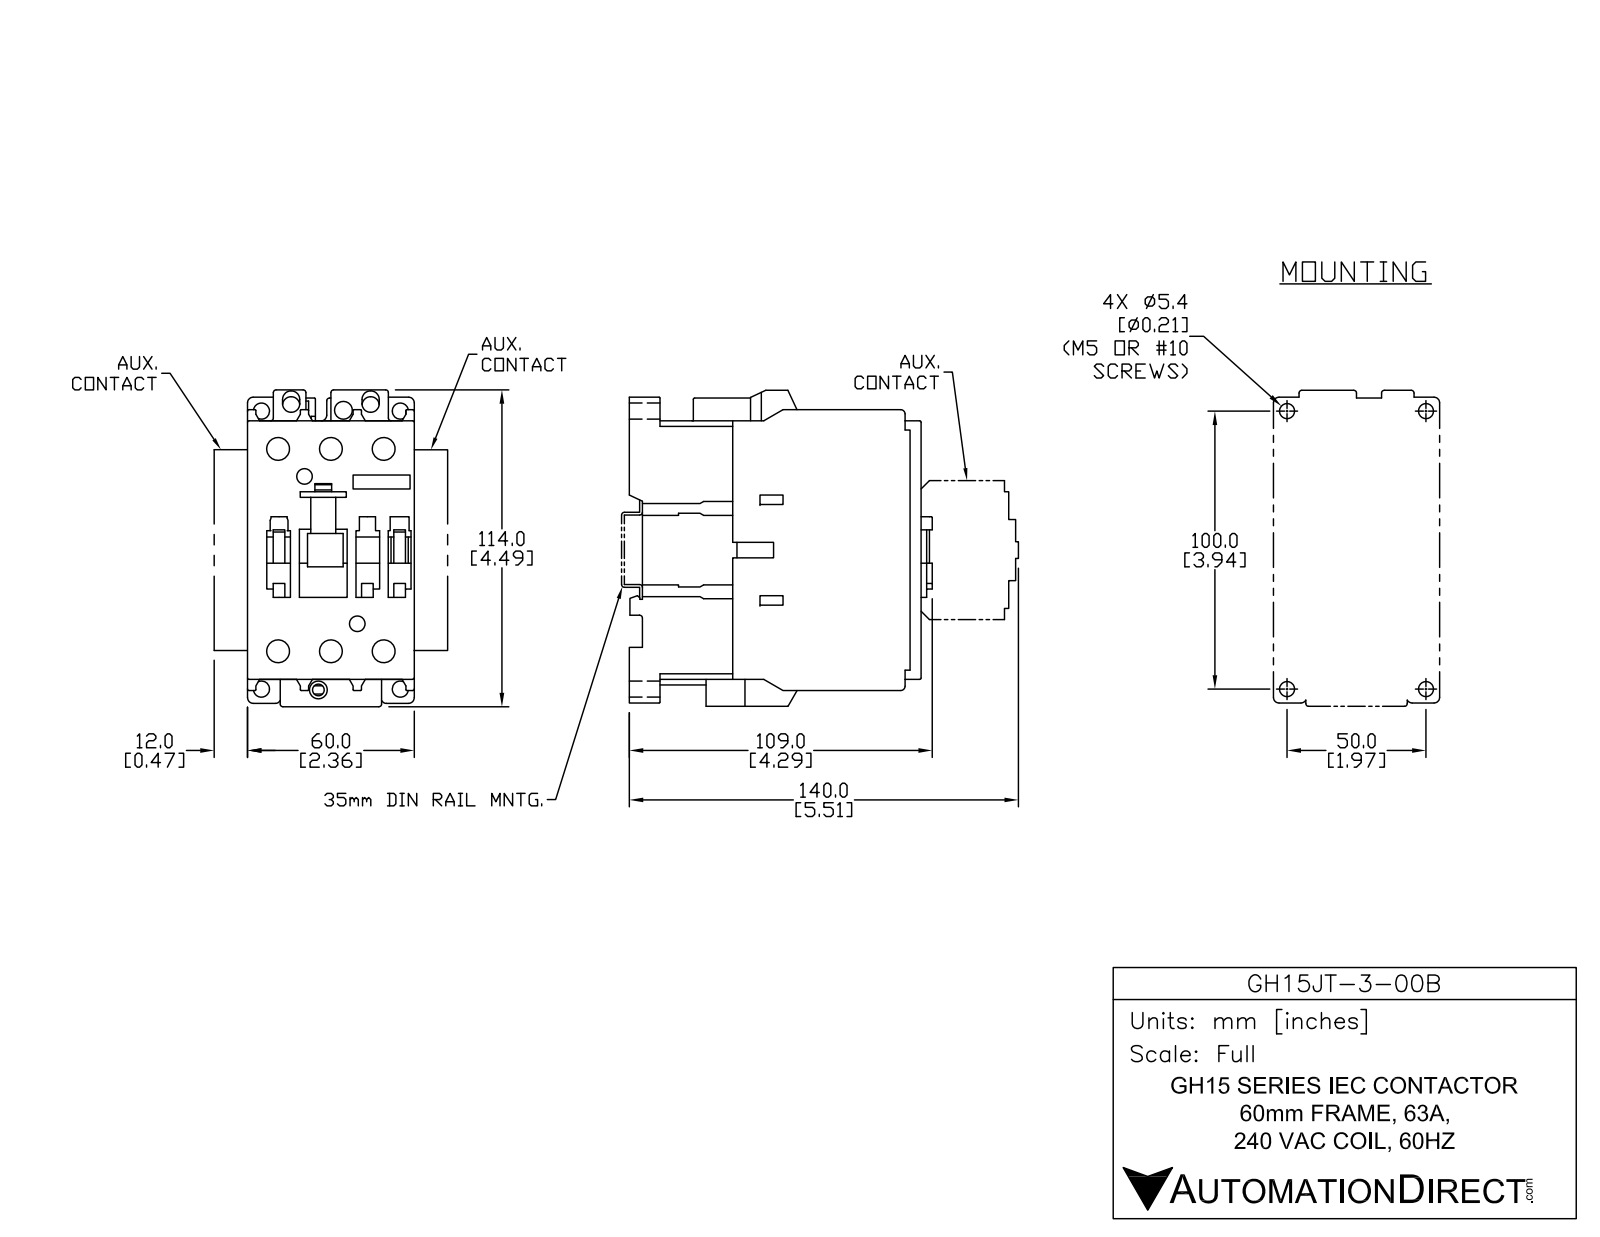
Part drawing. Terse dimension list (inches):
name: GH15JT-3-00B
written by: SolidWorks 2009 (AUTOMOTIVE_DESIGN)
unit: in
bodies: 1 solid, 836 faces (632 planar, 40 cylindrical, 164 other)
size: 4.488 × 4.321 × 2.362
volume: 34.24 in³; area: 105.1 in²
holes: 6× ⌀0.335, 4× ⌀0.236, 1× ⌀0.197, 1× ⌀0.242, 1× ⌀0.256
rounds: 10× R0.079, 2× R0.048, 2× R0.049
face distances: 2.362, 0.748, 3.917, 3.661, 0.413, 1.496, 0.335, 0.197, 0.807, 2.648
hole spacings: 3.535, 0.591, 0.748, 1.123, 1.815, 2.951, 3.404, 3.812
